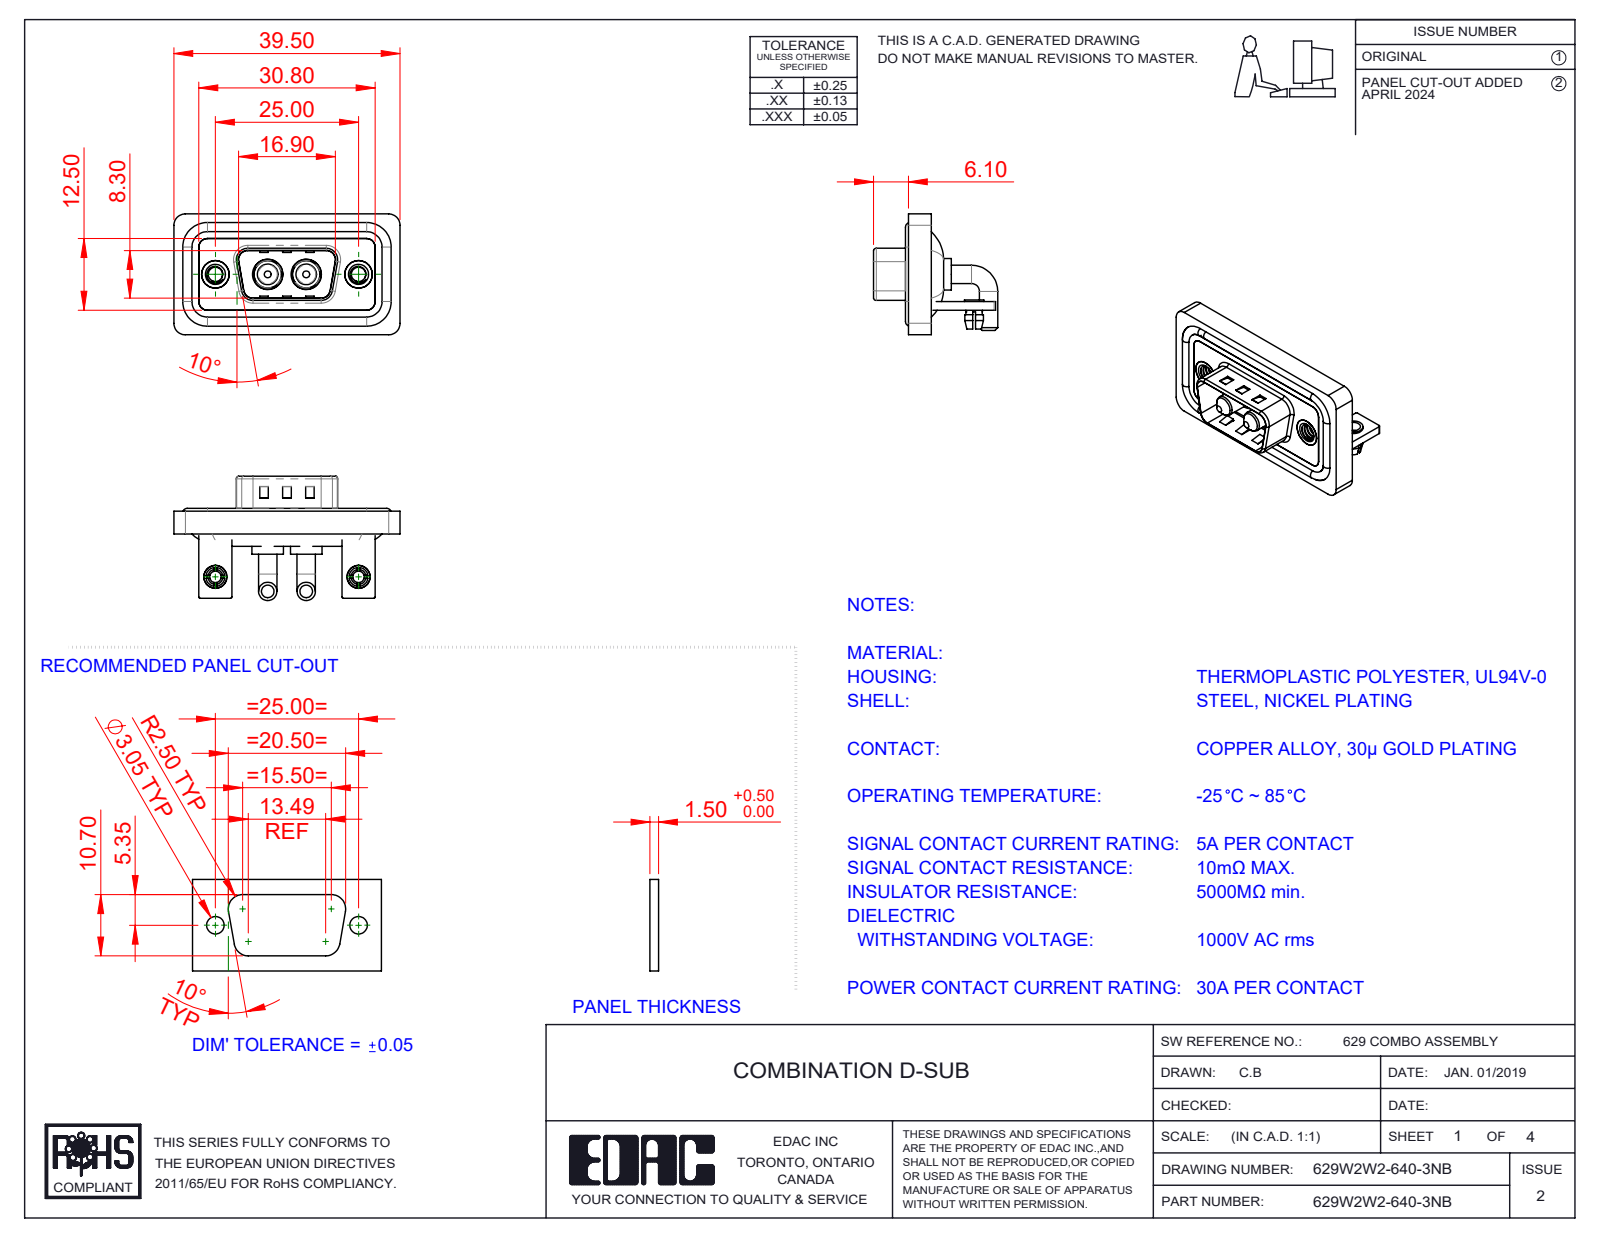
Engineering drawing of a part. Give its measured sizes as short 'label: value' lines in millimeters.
name: 629Combo Waterproof Housing_09 Contacts; 629W2W2-640-3NB; 629Combo Shell Rear_09 Contacts; 629Combo Threaded Rivet_B (+5 more)
written by: SolidWorks 2023 (CONFIG_CONTROL_DESIGN)
unit: mm
bodies: 15 solids, 627 faces (233 planar, 272 cylindrical, 122 other)
size: 39.5 × 21.7 × 21.1
volume: 4 949 mm³; area: 8 003 mm²
holes: 4× ⌀2.5, 2× ⌀2, 2× ⌀3.2, 2× ⌀4, 2× ⌀4.8, 2× ⌀4.85, 2× ⌀5, 2× ⌀5.3
bosses: 4× ⌀3.2, 4× ⌀1.6, 2× ⌀5.5, 2× ⌀5.2, 2× ⌀4.9, 2× ⌀4.75, 2× ⌀4, 2× ⌀3.75
rounds: 19× R2, 18× R1.5, 16× R0.25, 9× R0.5, 8× R1.6, 4× R0.6, 4× R0.65, 4× R0.9
face distances: 0.4, 1.5, 2.9, 0.8, 1.1, 1.2, 2.1, 1.6, 3.7, 2.5
hole spacings: 9.14, 15.86, 25, 6.72
